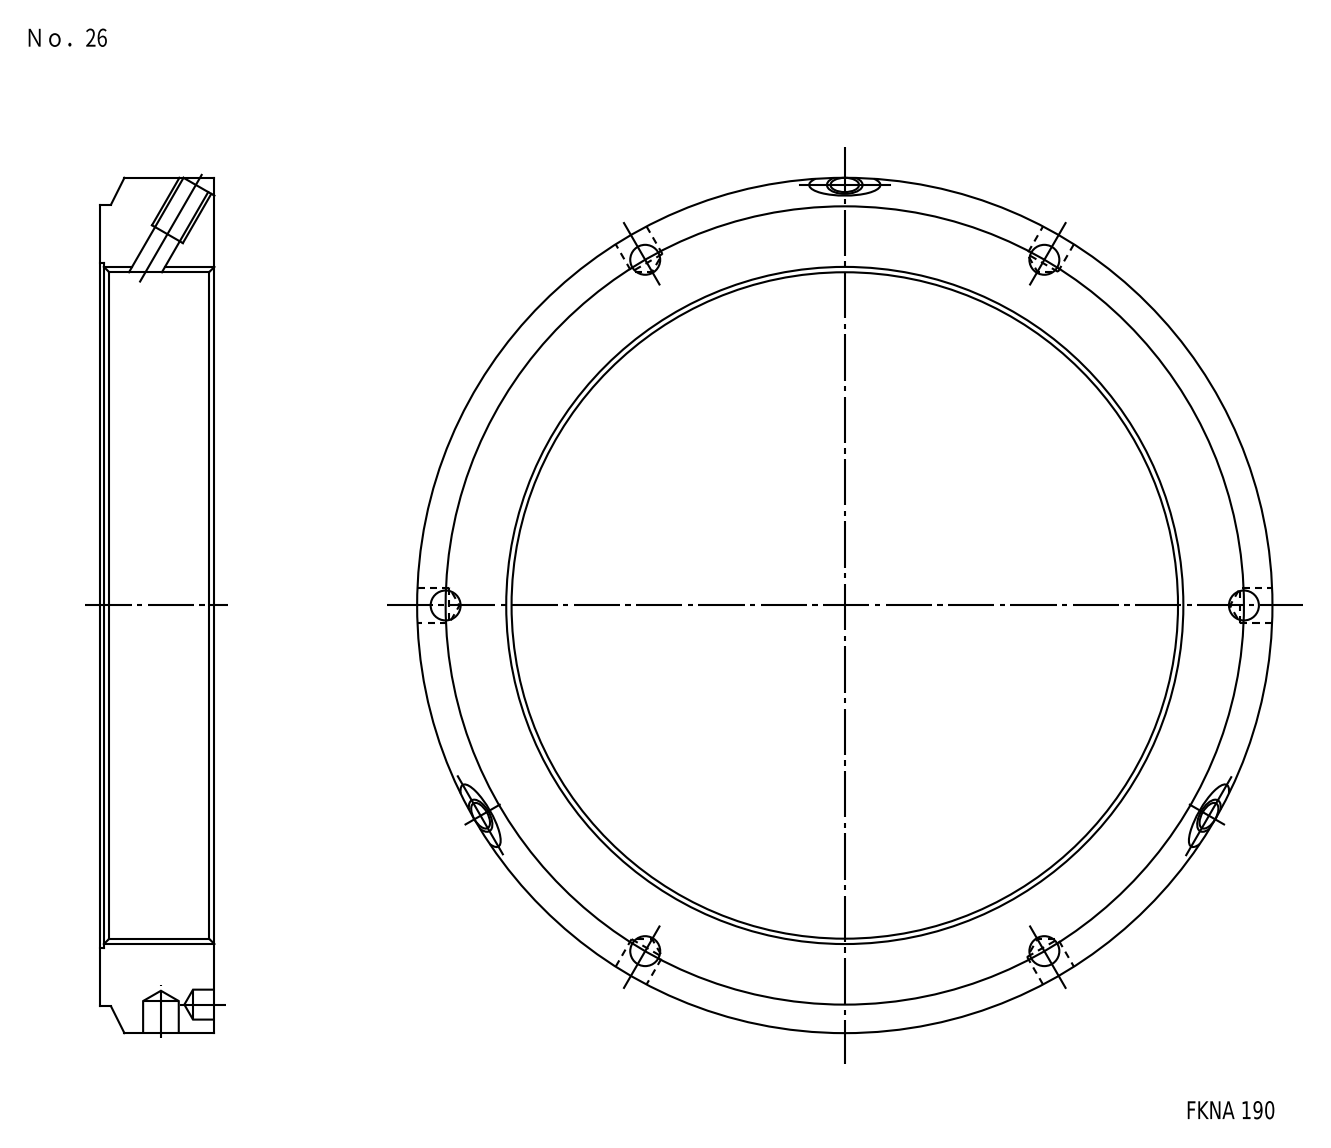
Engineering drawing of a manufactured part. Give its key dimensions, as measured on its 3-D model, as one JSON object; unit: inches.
{"part_name": "FKD FKNA190", "step_written_by": "Autodesk Inventor LT (CONFIG_CONTROL_DESIGN)", "units": "inches", "bodies": {"solids": 1, "faces": 44, "planar": 6, "cylindrical": 25, "other": 13}, "overall_size": [9.449, 9.449, 1.26], "volume_in3": 31.09, "surface_area_in2": 122.2, "round_holes": [[0.331, 6], [0.394, 5], [0.33, 3], [0.402, 3], [7.48, 1], [7.559, 1]], "round_bosses_or_shafts": [[9.449, 1], [8.858, 1]], "partial_cylinders_radius": [[0.787, 3]], "face_to_face_distances": [1.26, 0.059, 1.201], "hole_center_spacings": [4.409, 7.637, 7.637, 8.819, 8.819]}
